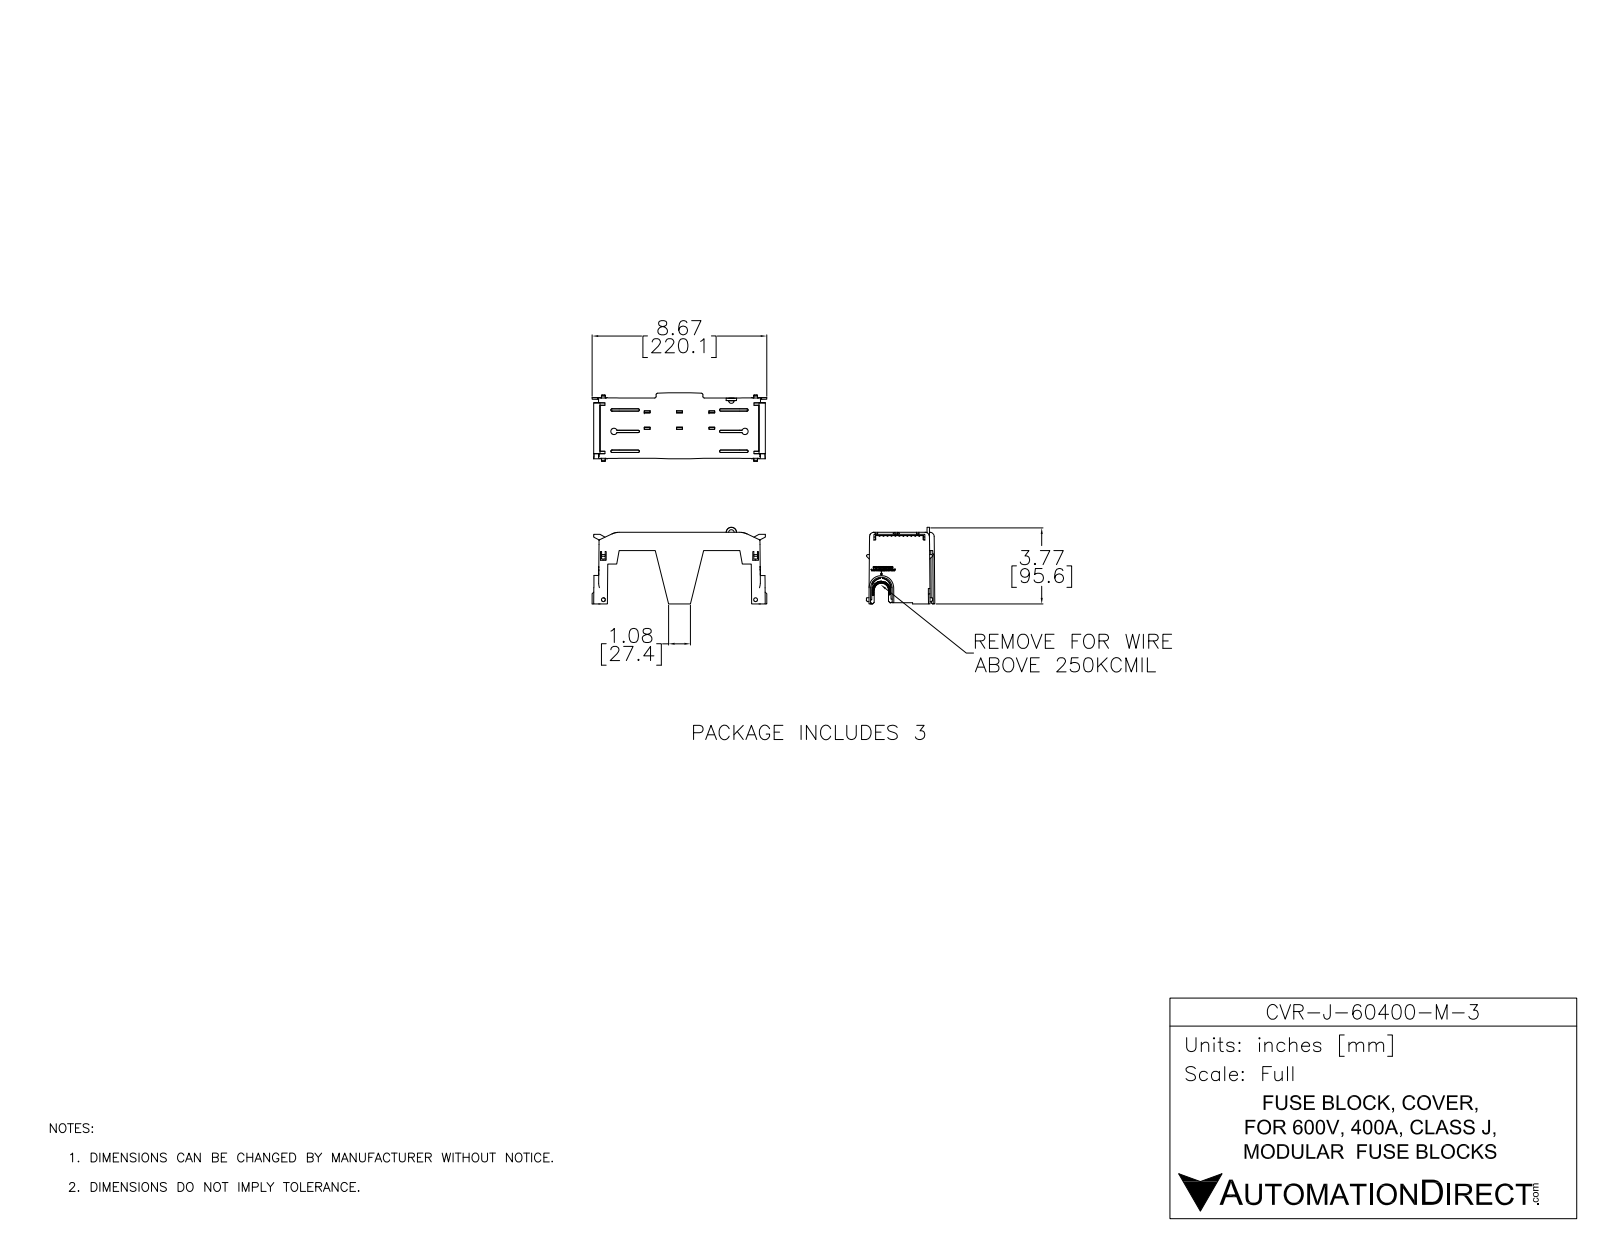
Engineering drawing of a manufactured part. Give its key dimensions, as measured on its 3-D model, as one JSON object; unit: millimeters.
{"part_name": "CVR-J-60400-M-3", "step_written_by": "SolidWorks 2017 (AUTOMOTIVE_DESIGN)", "units": "millimeters", "bodies": {"solids": 1, "faces": 2395, "planar": 1608, "cylindrical": 122, "other": 665}, "overall_size": [220.1, 96.6, 86.3], "volume_mm3": 104800, "surface_area_mm2": 110400, "round_holes": [[7, 1]], "partial_cylinders_radius": [[1, 18], [3, 11], [3.5, 8], [5.5, 7], [2, 4], [0.3, 2], [0.5, 2], [1, 2]], "face_to_face_distances": [2, 6, 8, 4, 20.4, 3, 5, 17, 37.4, 88.3]}
